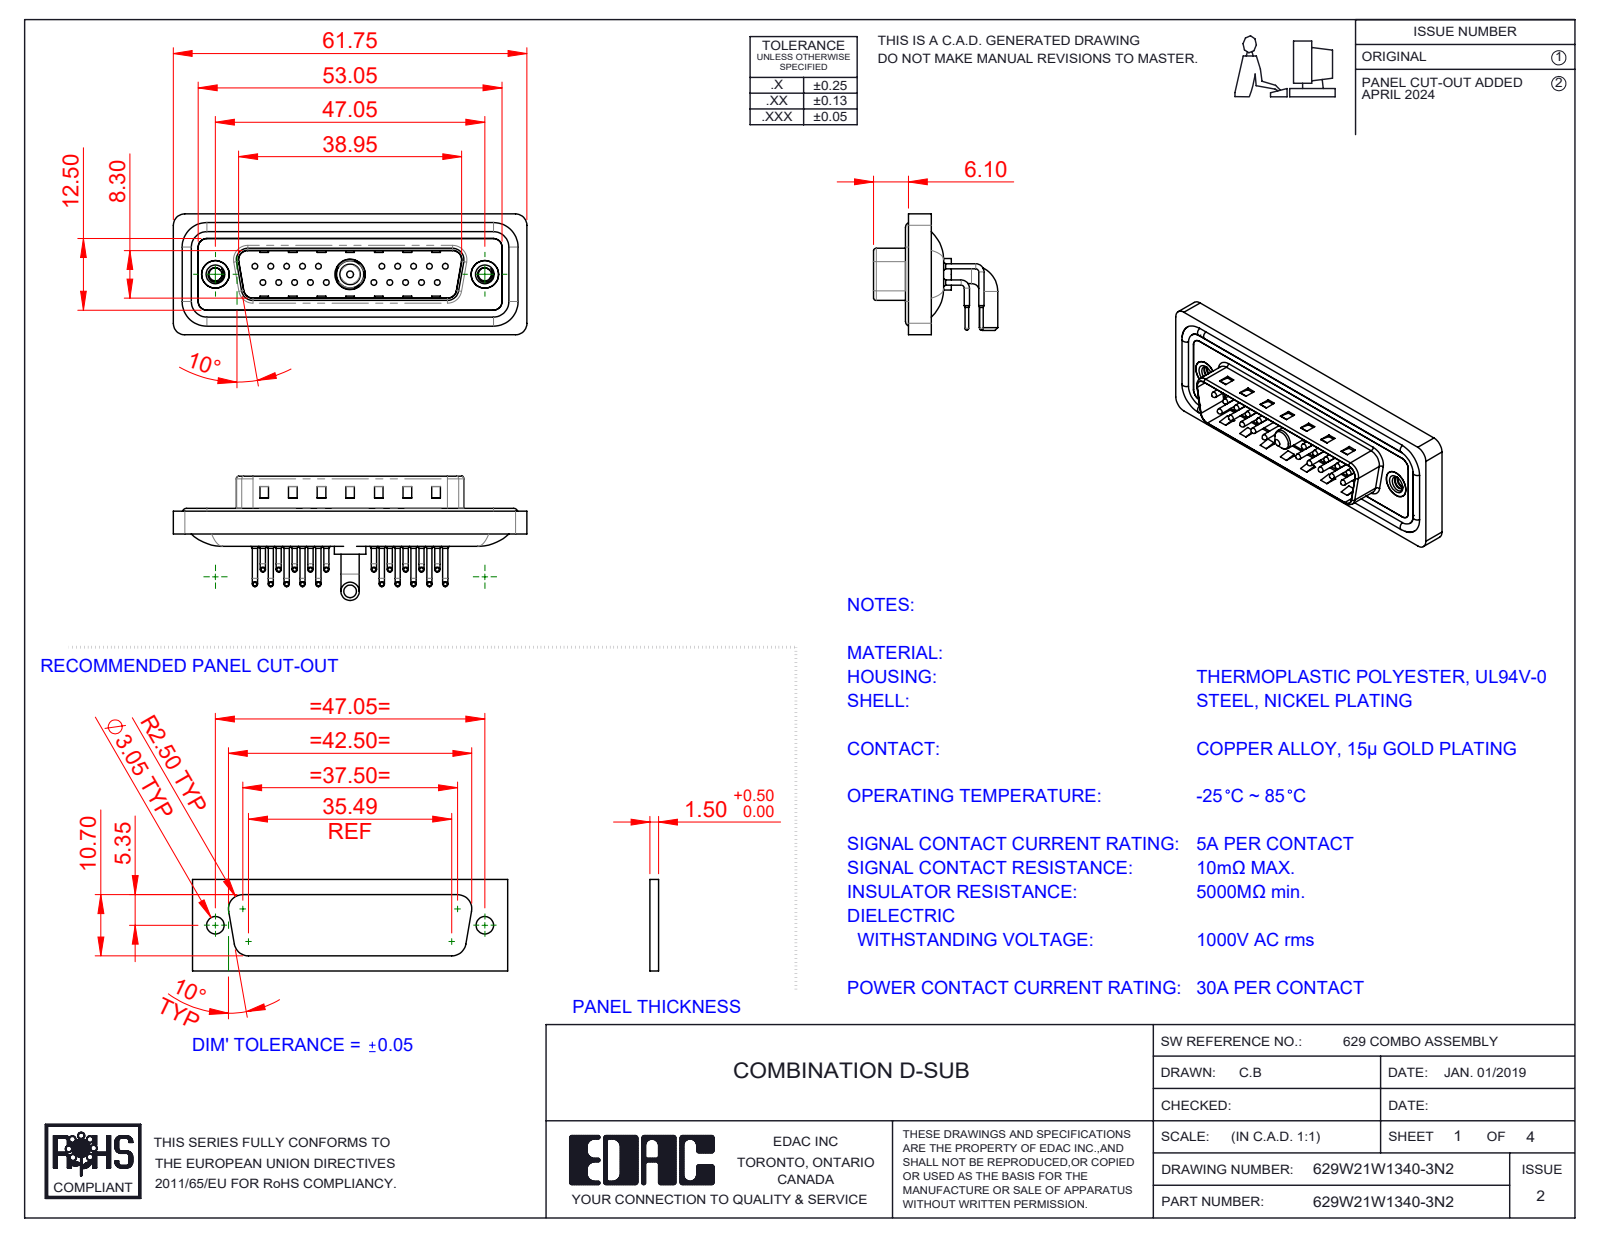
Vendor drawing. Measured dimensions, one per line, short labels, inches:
name: 629W21W1340-3N2; 629Combo Waterproof Housing_25 Contacts; 629Combo Contact Row 2; 629Combo Shell Rear_25 Contacts (+5 more)
written by: SolidWorks 2023 (CONFIG_CONTROL_DESIGN)
unit: in
bodies: 29 solids, 2726 faces (1499 planar, 929 cylindrical, 298 other)
size: 2.431 × 0.854 × 0.831
volume: 0.455 in³; area: 19.75 in²
holes: 20× ⌀0.03, 20× ⌀0.063, 20× ⌀0.079, 2× ⌀0.089, 2× ⌀0.157, 2× ⌀0.189, 2× ⌀0.197, 1× ⌀0.191, 1× ⌀0.209
bosses: 40× ⌀0.035, 20× ⌀0.059, 20× ⌀0.039, 20× ⌀0.026, 4× ⌀0.063, 2× ⌀0.193, 2× ⌀0.126, 1× ⌀0.217
rounds: 20× R0.04, 18× R0.059, 18× R0.079, 8× R0.02, 8× R0.063, 4× R0.01, 4× R0.024, 4× R0.026
face distances: 0.016, 0.114, 0.031, 0.161, 0.043, 0.083, 0.063, 0.177, 0.059, 0.098
hole spacings: 0.124, 0.109, 0.218, 0.327, 0.198, 0.763, 0.826, 0.872
